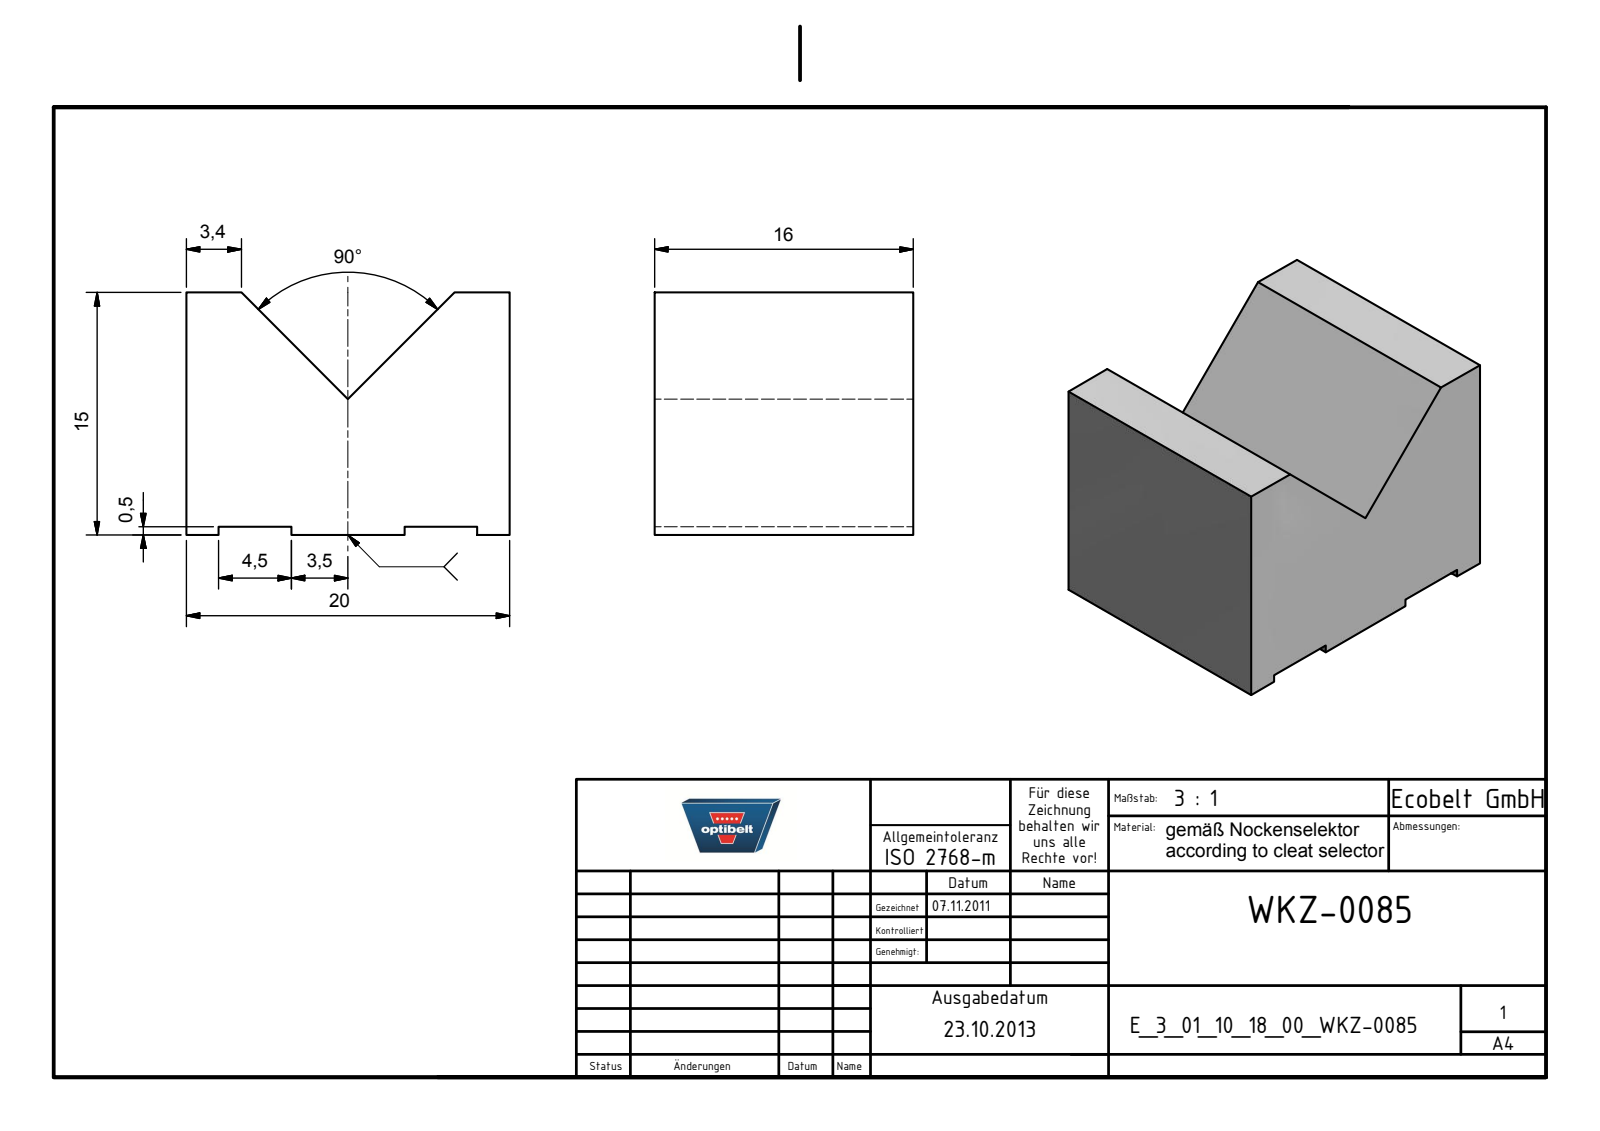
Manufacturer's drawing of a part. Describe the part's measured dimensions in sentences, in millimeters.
The part is named "E_3_01_10_18_00_WKZ-0085". Its 3-D file was written by "Autodesk Inventor 2025 (AUTOMOTIVE_DESIGN)". It is 1 solid with 17 faces: 17 planar, 0 cylindrical and 0 other. Overall it measures 20 by 16 by 15 millimeters. Its volume is 4 031 cubic millimeters and its surface area 1 743 square millimeters. The main face-to-face distances are 16, 20, 0.5, 15, 14.5, 2, 6.5, 13.5, 18, 4.5.
